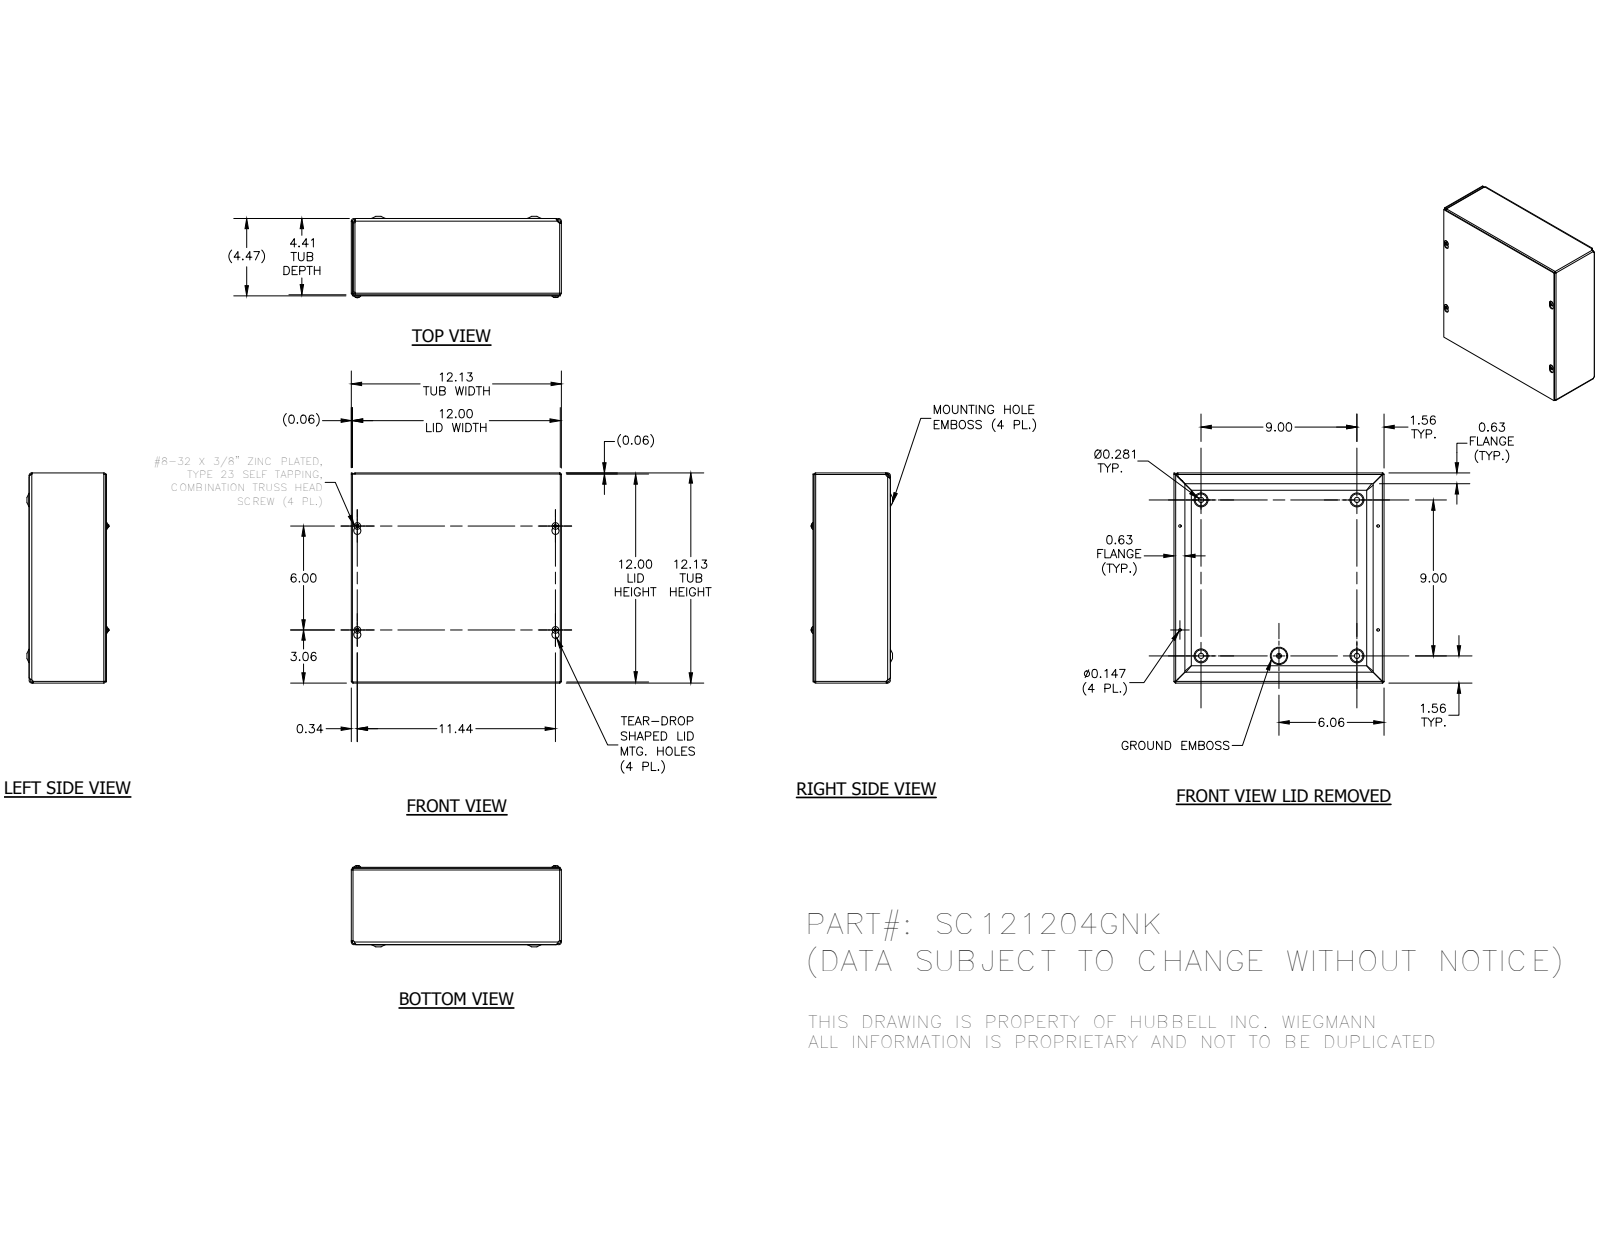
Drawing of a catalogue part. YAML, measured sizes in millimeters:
part_name: "SC1212GNKBKP; SC121204GNKWRA; SC1212GNKLID; 34056 (+1 more)"
step_written_by: "Autodesk Inventor 2014 (AUTOMOTIVE_DESIGN)"
units: millimeters
bodies: {solids: 7, faces: 358, planar: 133, cylindrical: 73, other: 152}
overall_size: [307.98, 307.98, 119.2]
volume: 567409
surface_area: 728511
round_holes:
  - {diameter: 3.73, count: 4}
  - {diameter: 7.62, count: 4}
  - {diameter: 4.19, count: 1}
round_bosses_or_shafts:
  - {diameter: 9.75, count: 4}
  - {diameter: 4.17, count: 4}
  - {diameter: 5.8, count: 1}
partial_cylinders:
  - {radius: 0.79, count: 8}
  - {radius: 2.37, count: 8}
  - {radius: 1.4, count: 4}
  - {radius: 1.57, count: 4}
  - {radius: 2.38, count: 4}
  - {radius: 2.97, count: 4}
  - {radius: 3.15, count: 4}
  - {radius: 3.17, count: 4}
face_to_face_distances: [1.57, 110.32, 306.4, 111.89, 1.59, 111.91, 113.48, 304.83, 1.58, 307.98]
hole_center_spacings: [228.6, 114.3, 152.4, 192.98, 193.02, 255.58, 262.33, 262.34]
